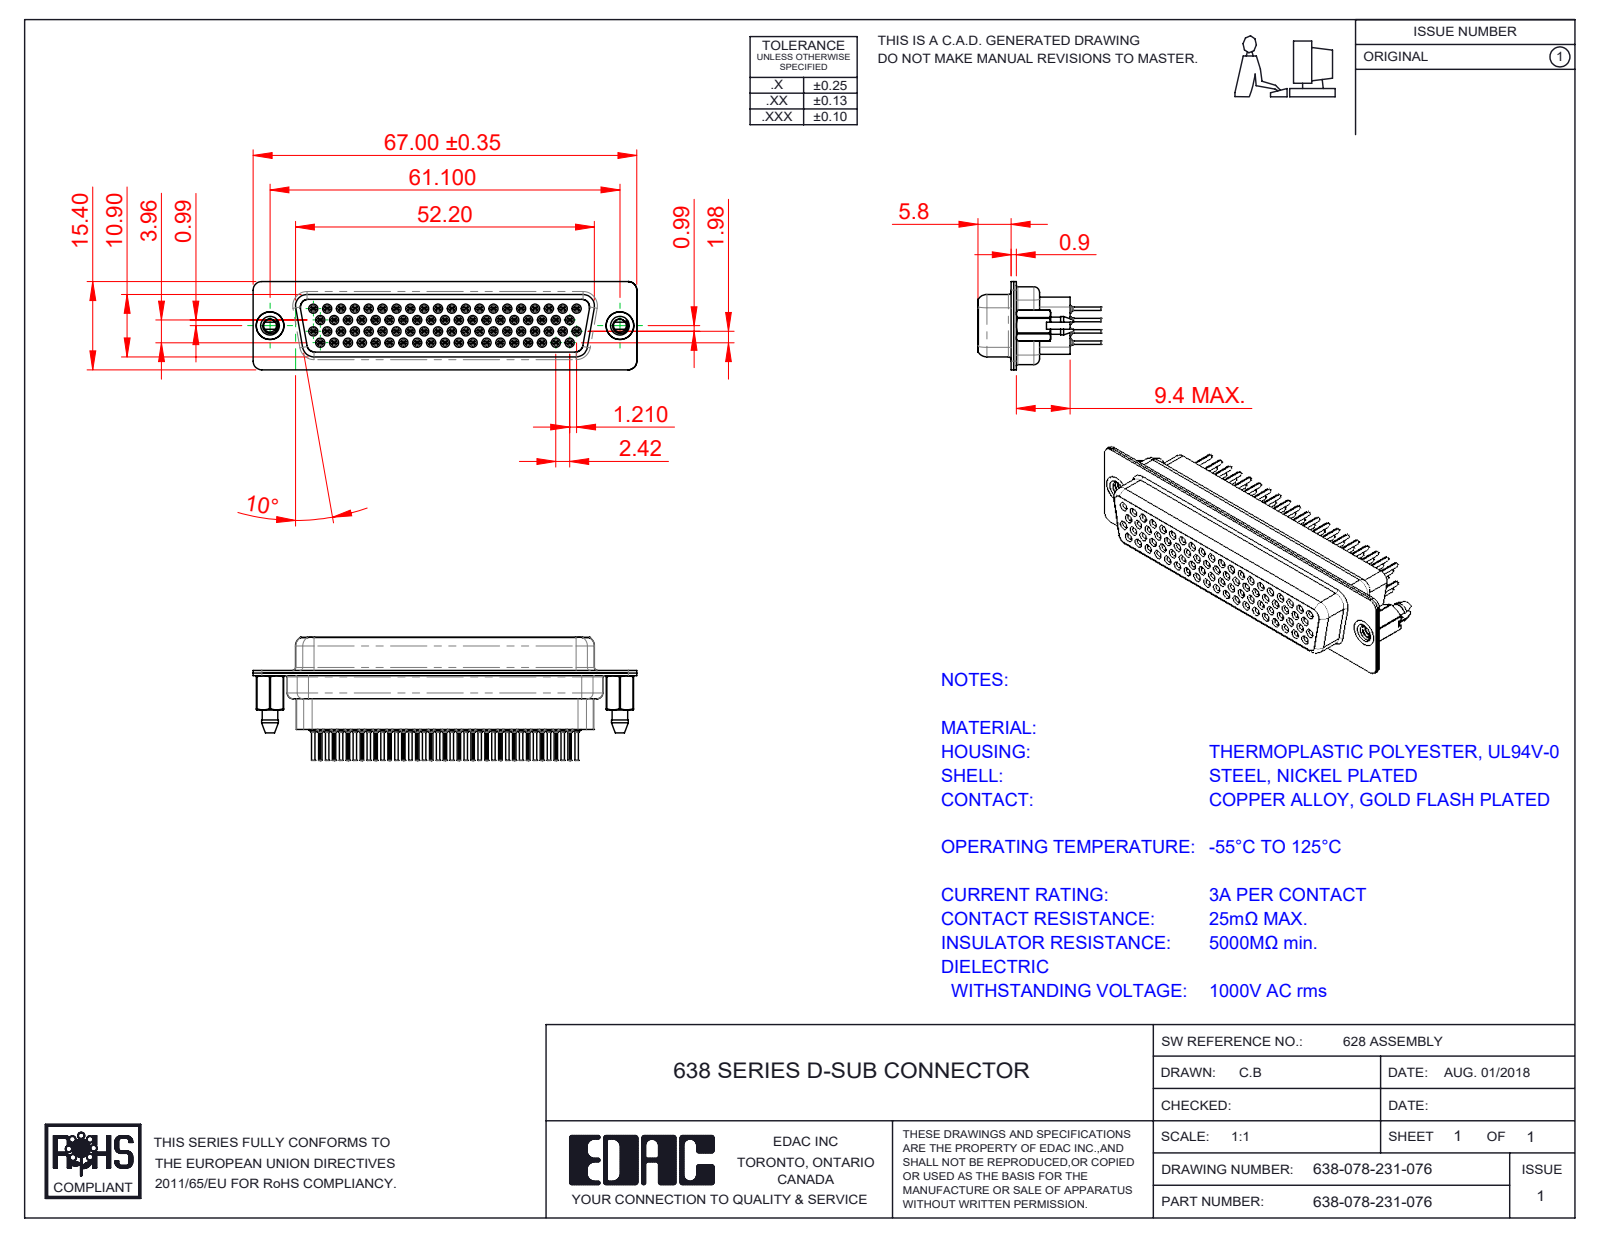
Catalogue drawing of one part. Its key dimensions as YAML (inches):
part_name: "638 Contact Row 2_31; 638 Contact Row 3_31; 638 Housing_78 Contacts HP; 638 Contact Row 78_31 (+5 more)"
step_written_by: "SolidWorks 2020 (CONFIG_CONTROL_DESIGN)"
units: inches
bodies: {solids: 83, faces: 9947, planar: 2517, cylindrical: 2743, other: 4687}
overall_size: [2.638, 0.846, 0.606]
volume: 0.453
surface_area: 39.21
round_holes:
  - {diameter: 0.008, count: 78}
  - {diameter: 0.031, count: 78}
  - {diameter: 0.039, count: 78}
  - {diameter: 0.043, count: 78}
  - {diameter: 0.063, count: 78}
  - {diameter: 0.067, count: 78}
  - {diameter: 0.071, count: 78}
  - {diameter: 0.089, count: 2}
  - {diameter: 0.157, count: 2}
  - {diameter: 0.159, count: 2}
  - {diameter: 0.191, count: 2}
round_bosses_or_shafts:
  - {diameter: 0.079, count: 78}
  - {diameter: 0.059, count: 78}
  - {diameter: 0.047, count: 78}
  - {diameter: 0.024, count: 78}
  - {diameter: 0.195, count: 2}
  - {diameter: 0.189, count: 2}
  - {diameter: 0.157, count: 1}
partial_cylinders:
  - {radius: 0.004, count: 156}
  - {radius: 0.011, count: 39}
  - {radius: 0.059, count: 18}
  - {radius: 0.079, count: 12}
  - {radius: 0.061, count: 8}
  - {radius: 0.01, count: 4}
  - {radius: 0.02, count: 4}
  - {radius: 0.022, count: 4}
face_to_face_distances: [0.018, 0.016, 0.378, 0.035, 0.053, 0.465, 0.449, 0.071, 0.394, 0.406]
hole_center_spacings: [0.095, 0.191, 0.286, 0.381, 0.239, 0.476, 0.274, 0.334]
